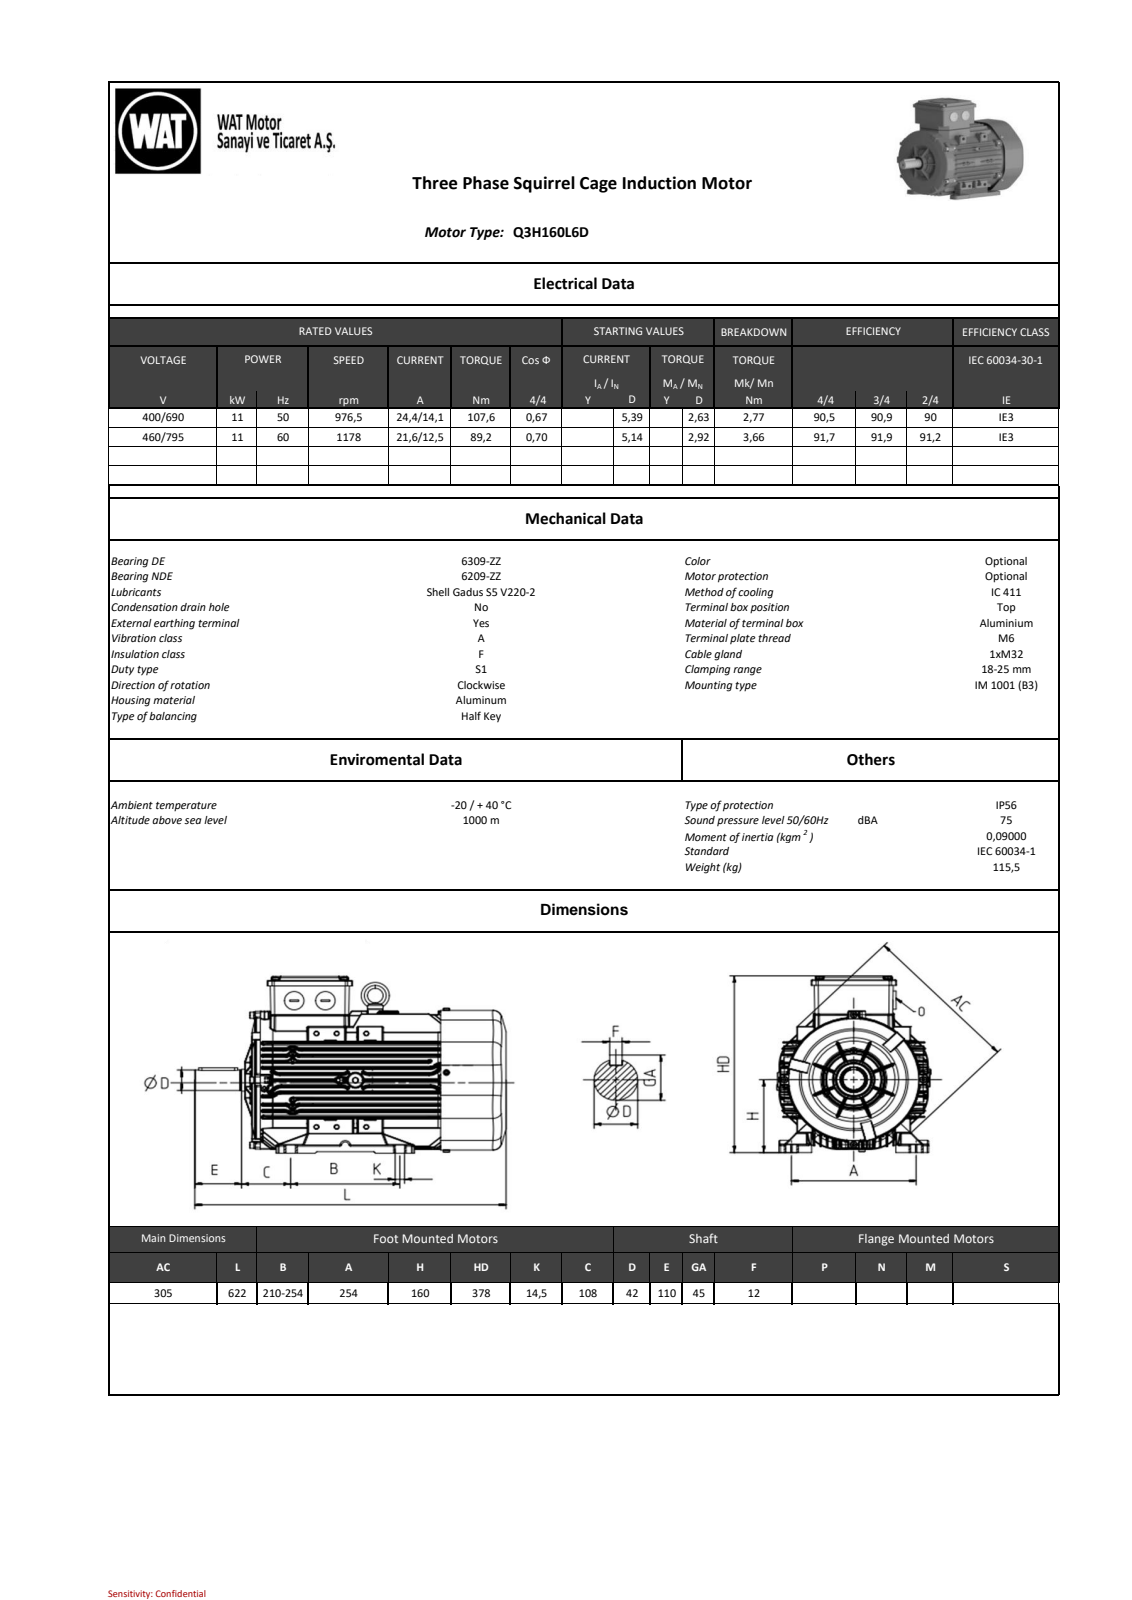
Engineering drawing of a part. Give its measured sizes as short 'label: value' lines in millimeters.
name: AB_objects
written by: SIEMENS PLM Software NX2206.8101 (AP203_CONFIGURATION_CONTROLLED_3D_DESIGN_OF_MECHANICAL_PARTS_AND_ASSEMBLIES_MIM_LF)
unit: mm
bodies: 0 solids, 8341 faces (2321 planar, 3173 cylindrical, 2847 other)
size: 618.92 × 377.75 × 314
holes: 1× ⌀10, 1× ⌀14, 1× ⌀17, 1× ⌀72, 1× ⌀85.63, 1× ⌀94, 1× ⌀114, 1× ⌀134, 1× ⌀154, 1× ⌀174, 1× ⌀194
bosses: 4× ⌀16, 4× ⌀13, 4× ⌀10, 4× ⌀8, 2× ⌀38, 1× ⌀272.5, 1× ⌀178, 1× ⌀168
rounds: 729× R1, 667× R0.5, 105× R1.5, 103× R4, 68× R5, 50× R2.5, 27× R3, 12× R5.5
face distances: 144, 168, 120, 11.92, 9.62, 14.77, 168.39, 158.77, 24.39, 11.85
hole spacings: 0.43
